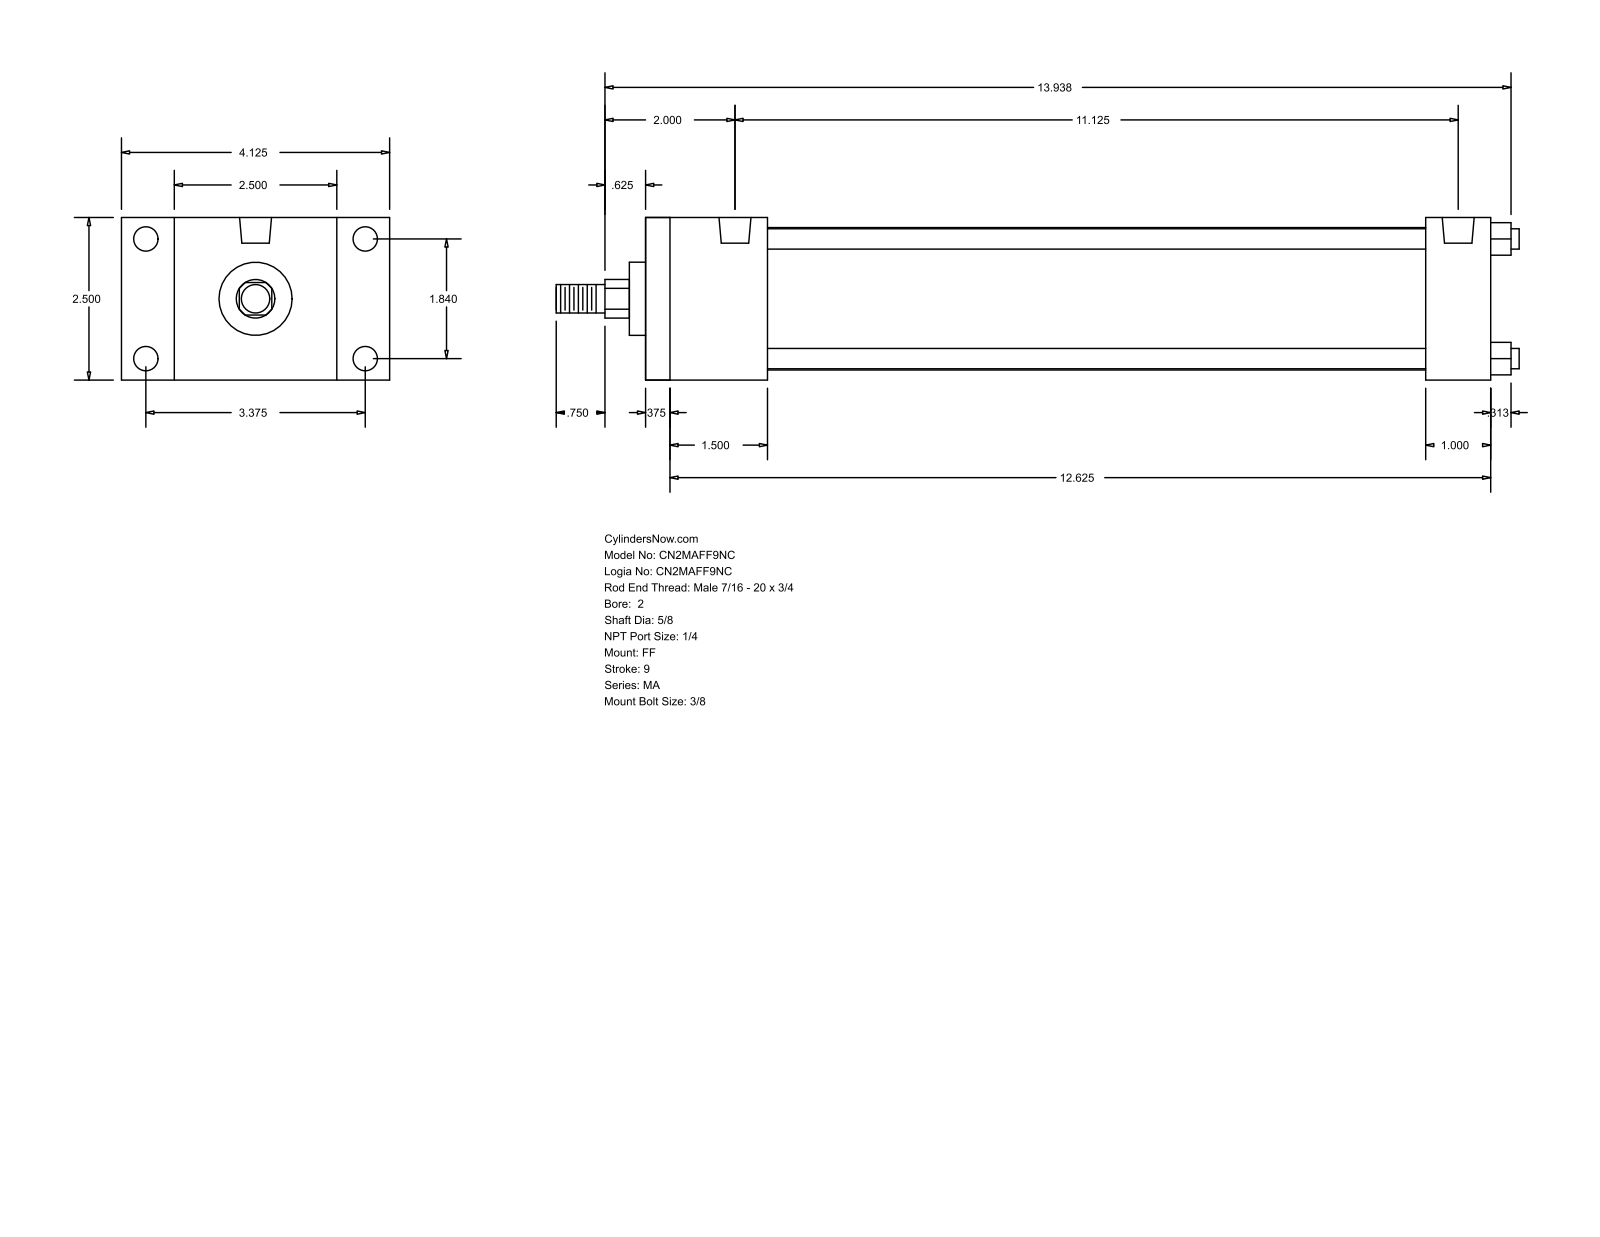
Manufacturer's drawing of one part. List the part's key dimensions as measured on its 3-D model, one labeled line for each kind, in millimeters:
Part name (STEP PRODUCT): MA_FF__0200_0.625
STEP written by: GSSL Pune (CONFIG_CONTROL_DESIGN)
Units: millimetres
Bodies: 0 solids, 92 faces (64 planar, 28 cylindrical, 0 other)
Overall size (bounding box): 376.24 × 104.78 × 63.5
Round holes (diameter × count): ⌀7.94 ×4, ⌀9.53 ×4, ⌀12.49 ×2
Round bosses / shafts (diameter × count): ⌀7.94 ×4, ⌀55.63 ×1, ⌀28.57 ×1, ⌀15.88 ×1, ⌀11.11 ×1
Partial cylindrical surfaces — rounded edges, fillets, slot ends (radius × count): R7.54 ×1
Main face-to-face distances: 63.5, 330.19, 9.52, 320.67, 38.1, 47.62, 304.8, 295.28, 257.18, 282.57
Hole centre spacings: 46.74, 85.72, 97.63, 282.58
